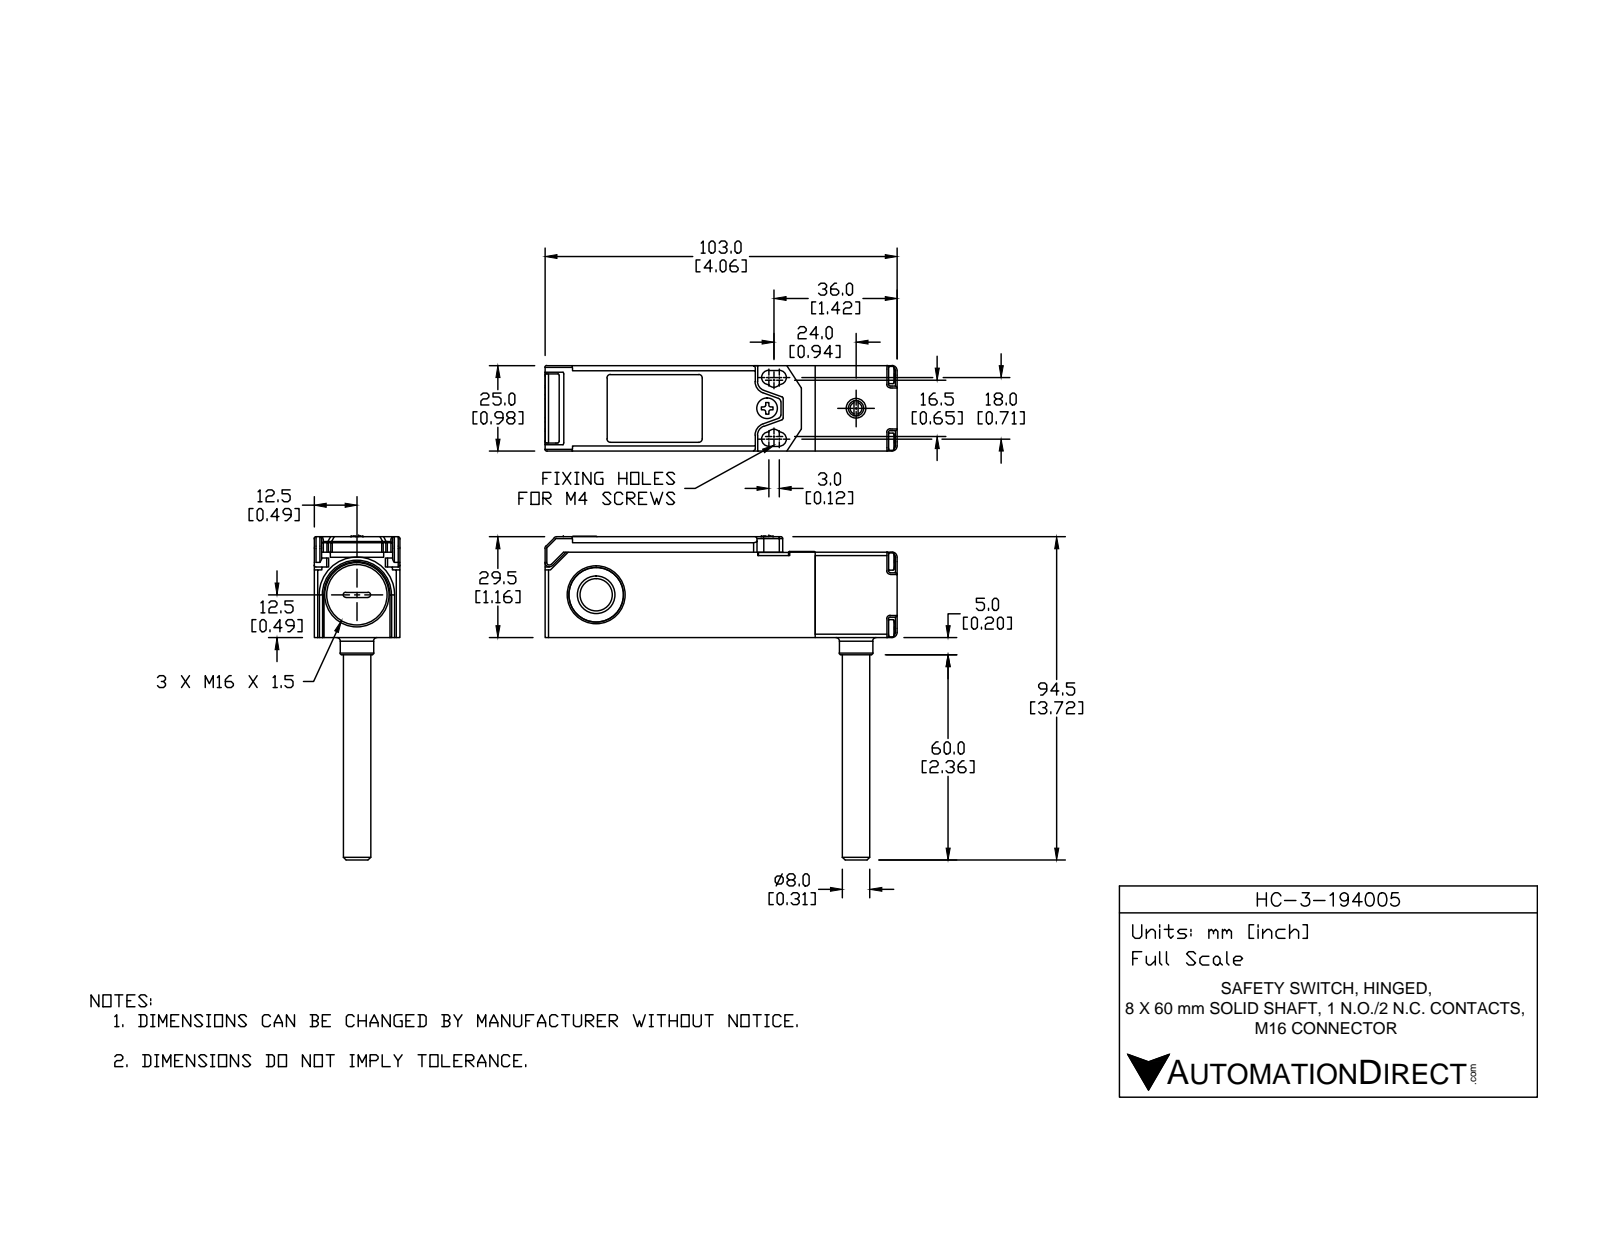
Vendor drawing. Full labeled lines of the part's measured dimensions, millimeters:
Part name (STEP PRODUCT): HC-3-194005
STEP written by: SolidWorks 2014 (AUTOMOTIVE_DESIGN)
Units: millimetres
Bodies: 13 solids, 1848 faces (866 planar, 583 cylindrical, 399 other)
Overall size (bounding box): 103 × 94.7 × 25
Volume: 33 300 mm³ · Surface area: 33 040 mm²
Round holes (diameter × count): ⌀3.2 ×5, ⌀2.4 ×4, ⌀1.5 ×2, ⌀1.6 ×2, ⌀1.8 ×2, ⌀2.2 ×2, ⌀3.6 ×2, ⌀16 ×2, ⌀1.4 ×1, ⌀2.1 ×1, ⌀2.5 ×1, ⌀2.6 ×1
Round bosses / shafts (diameter × count): ⌀2.6 ×5, ⌀5 ×4, ⌀2 ×4, ⌀3.5 ×2, ⌀9.8 ×1, ⌀8 ×1, ⌀6.5 ×1, ⌀5.8 ×1
Partial cylindrical surfaces — rounded edges, fillets, slot ends (radius × count): R0.5 ×225, R0.1 ×24, R1 ×21, R0.3 ×12, R1.5 ×6, R2.1 ×6, R2.8 ×6, R3.5 ×6
Main face-to-face distances: 25, 2, 1.8, 23.2, 4.5, 23, 2.5, 1, 21, 2.2
Hole centre spacings: 13.8, 19.5, 4.3, 4.7, 6.2, 10.5, 10.7, 10.8
